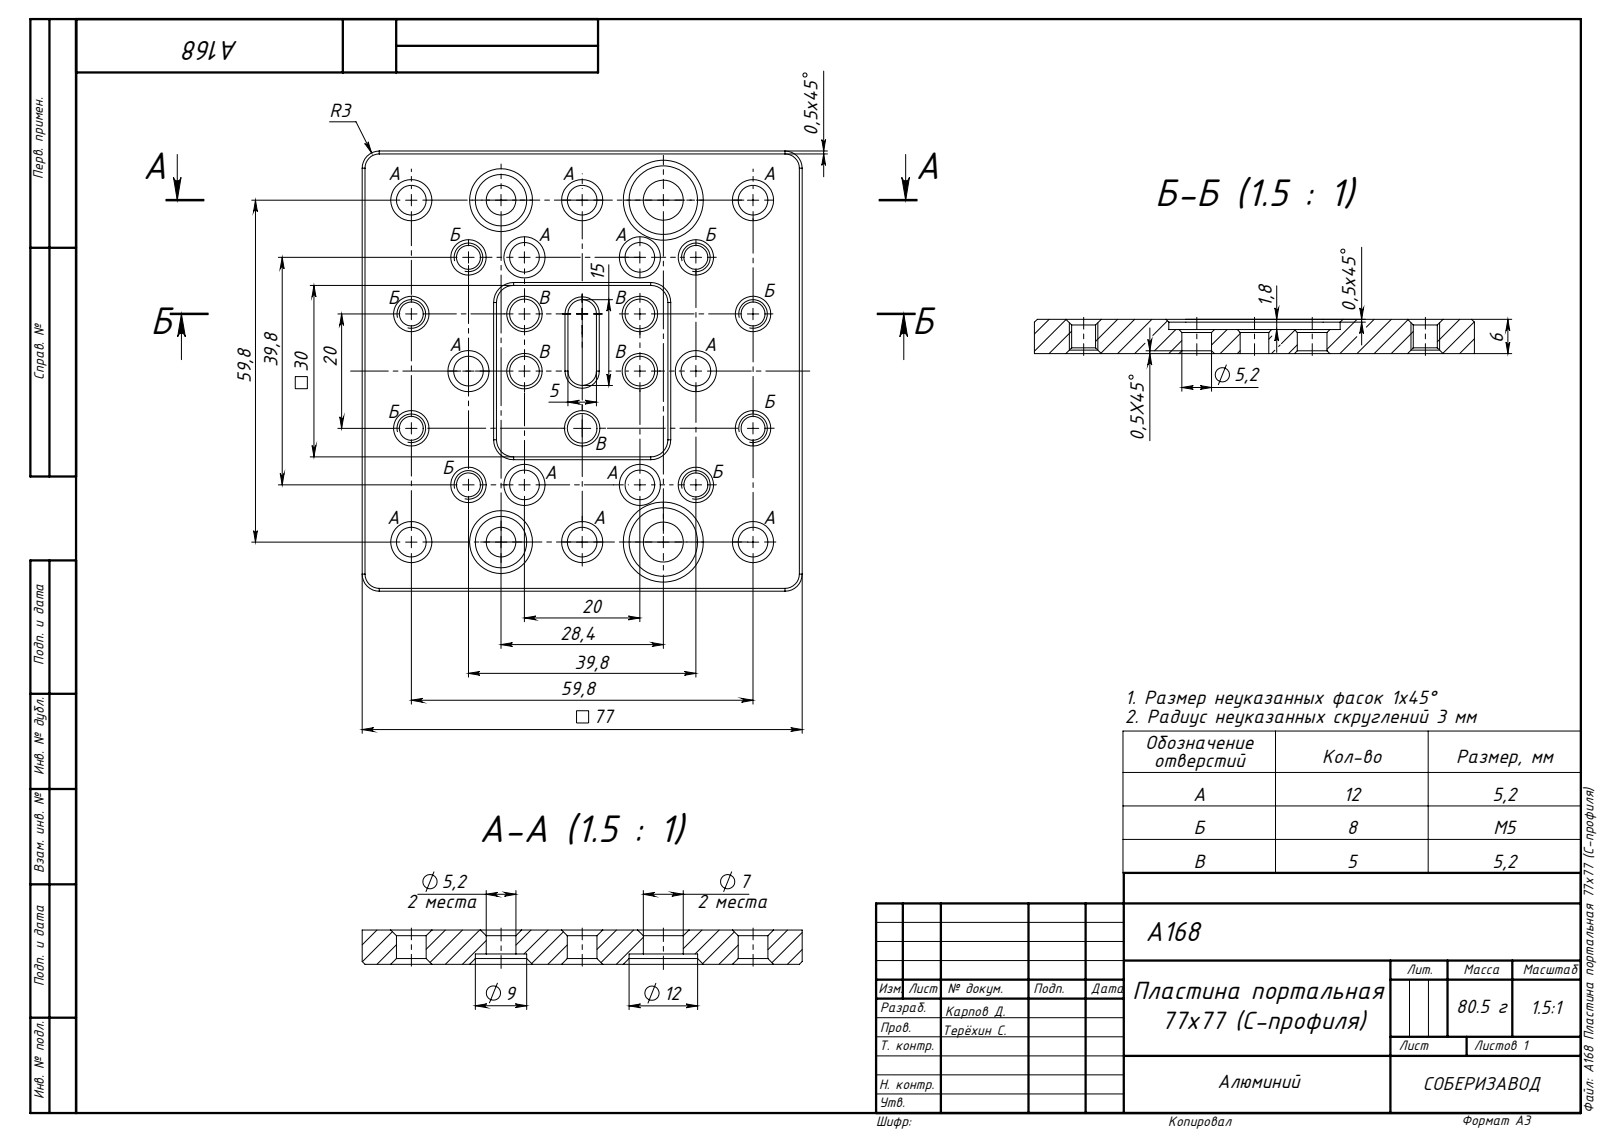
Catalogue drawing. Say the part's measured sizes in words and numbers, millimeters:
The part is named "A168 Пластина портальная 77х77 (С-профиля)". Its 3-D file was written by "SolidWorks 2018 (AUTOMOTIVE_DESIGN)". It is 1 solid with 229 faces: 27 planar, 76 cylindrical and 126 other. Overall it measures 77 by 77 by 6 millimeters. Its volume is 29 316 cubic millimeters and its surface area 14 816 square millimeters. Round holes: 19 of diameter 5.2, 8 of diameter 4.2, 2 of diameter 7, 2 of diameter 9, 2 of diameter 12. Partial cylindrical surfaces (rounded edges, fillets, slot ends): 8 of radius 3, 2 of radius 2.5. The main face-to-face distances are 6, 4.2, 1.8, 77, 23.5, 53.5, 36, 41, 37.83, 12.5. The hole center spacings are 22.18, 19.9, 35.92, 50.79, 14.14, 59.8, 29.9, 31.53.
